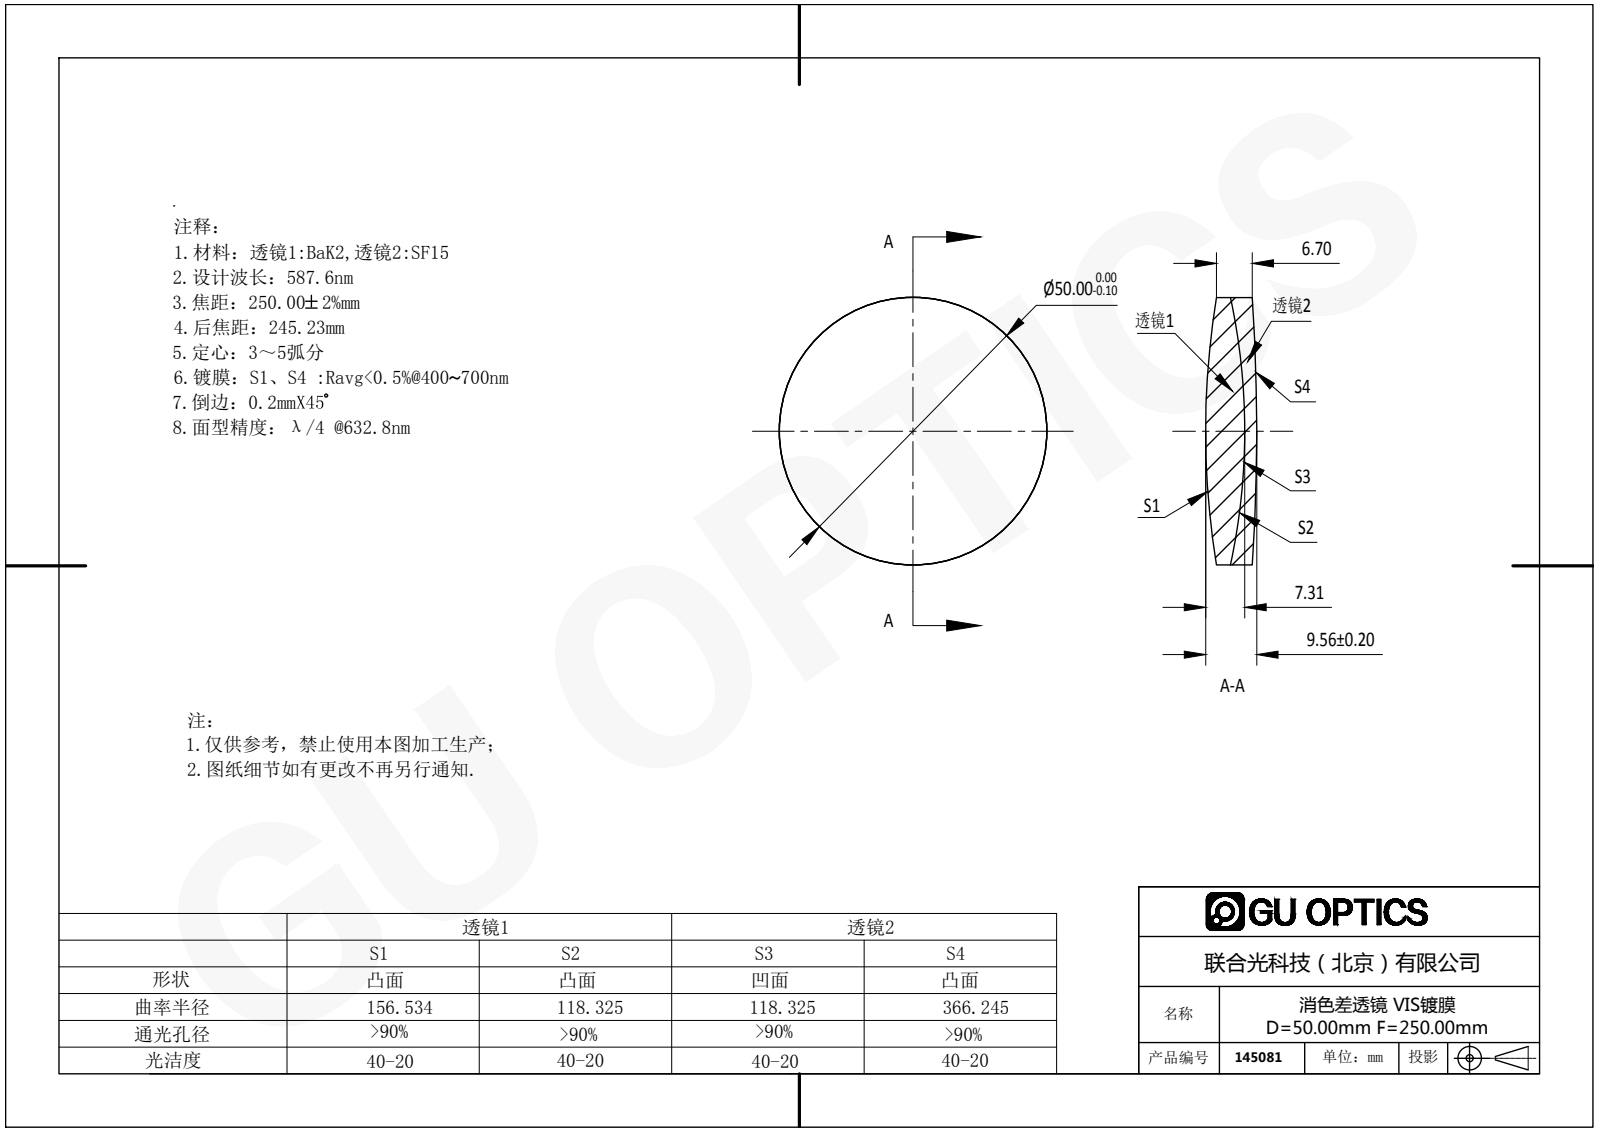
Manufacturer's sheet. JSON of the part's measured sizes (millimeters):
{"part_name": "145081", "step_written_by": "SolidWorks 2016 (AUTOMOTIVE_DESIGN)", "units": "millimeters", "bodies": {"solids": 2, "faces": 12, "planar": 0, "cylindrical": 4, "other": 8}, "overall_size": [50, 50, 9.56], "volume_mm3": 15964, "surface_area_mm2": 8966, "round_bosses_or_shafts": [[50, 1]]}
